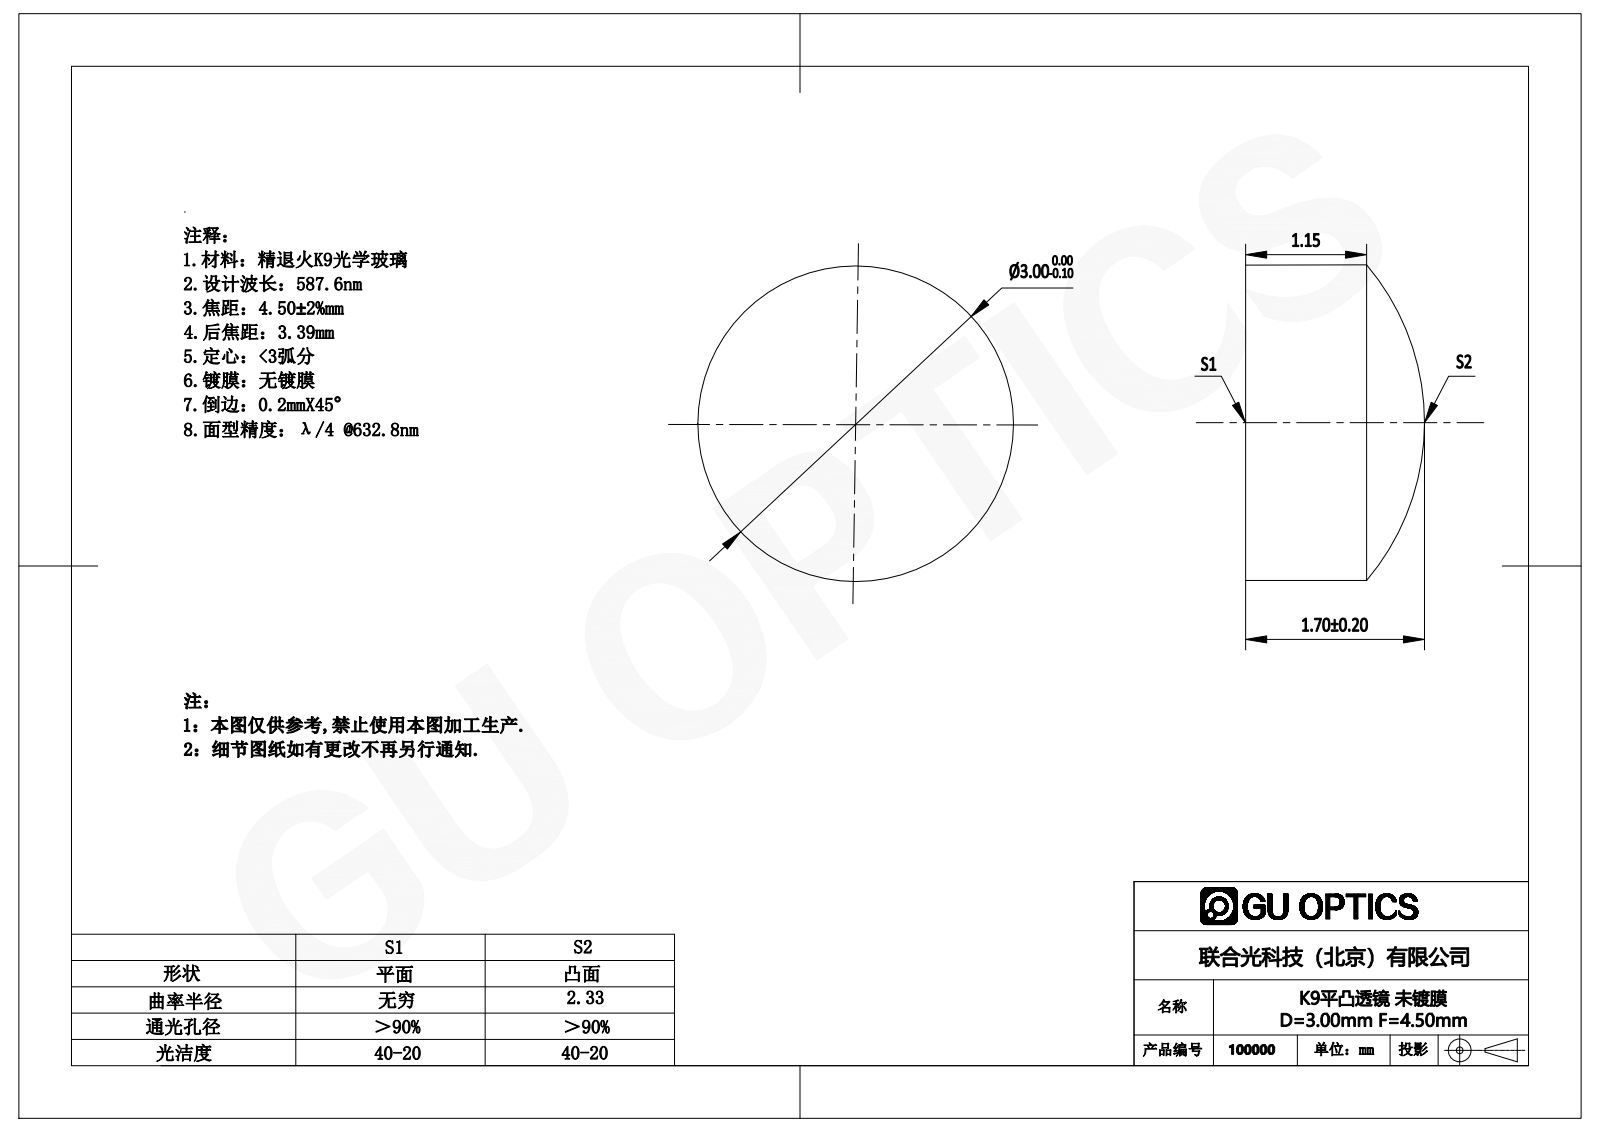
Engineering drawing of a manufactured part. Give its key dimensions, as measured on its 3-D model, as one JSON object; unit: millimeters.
{"part_name": "100000", "step_written_by": "SolidWorks 2016 (AUTOMOTIVE_DESIGN)", "units": "millimeters", "bodies": {"solids": 1, "faces": 5, "planar": 1, "cylindrical": 0, "other": 4}, "overall_size": [3, 3, 1.7], "volume_mm3": 10, "surface_area_mm2": 26}
